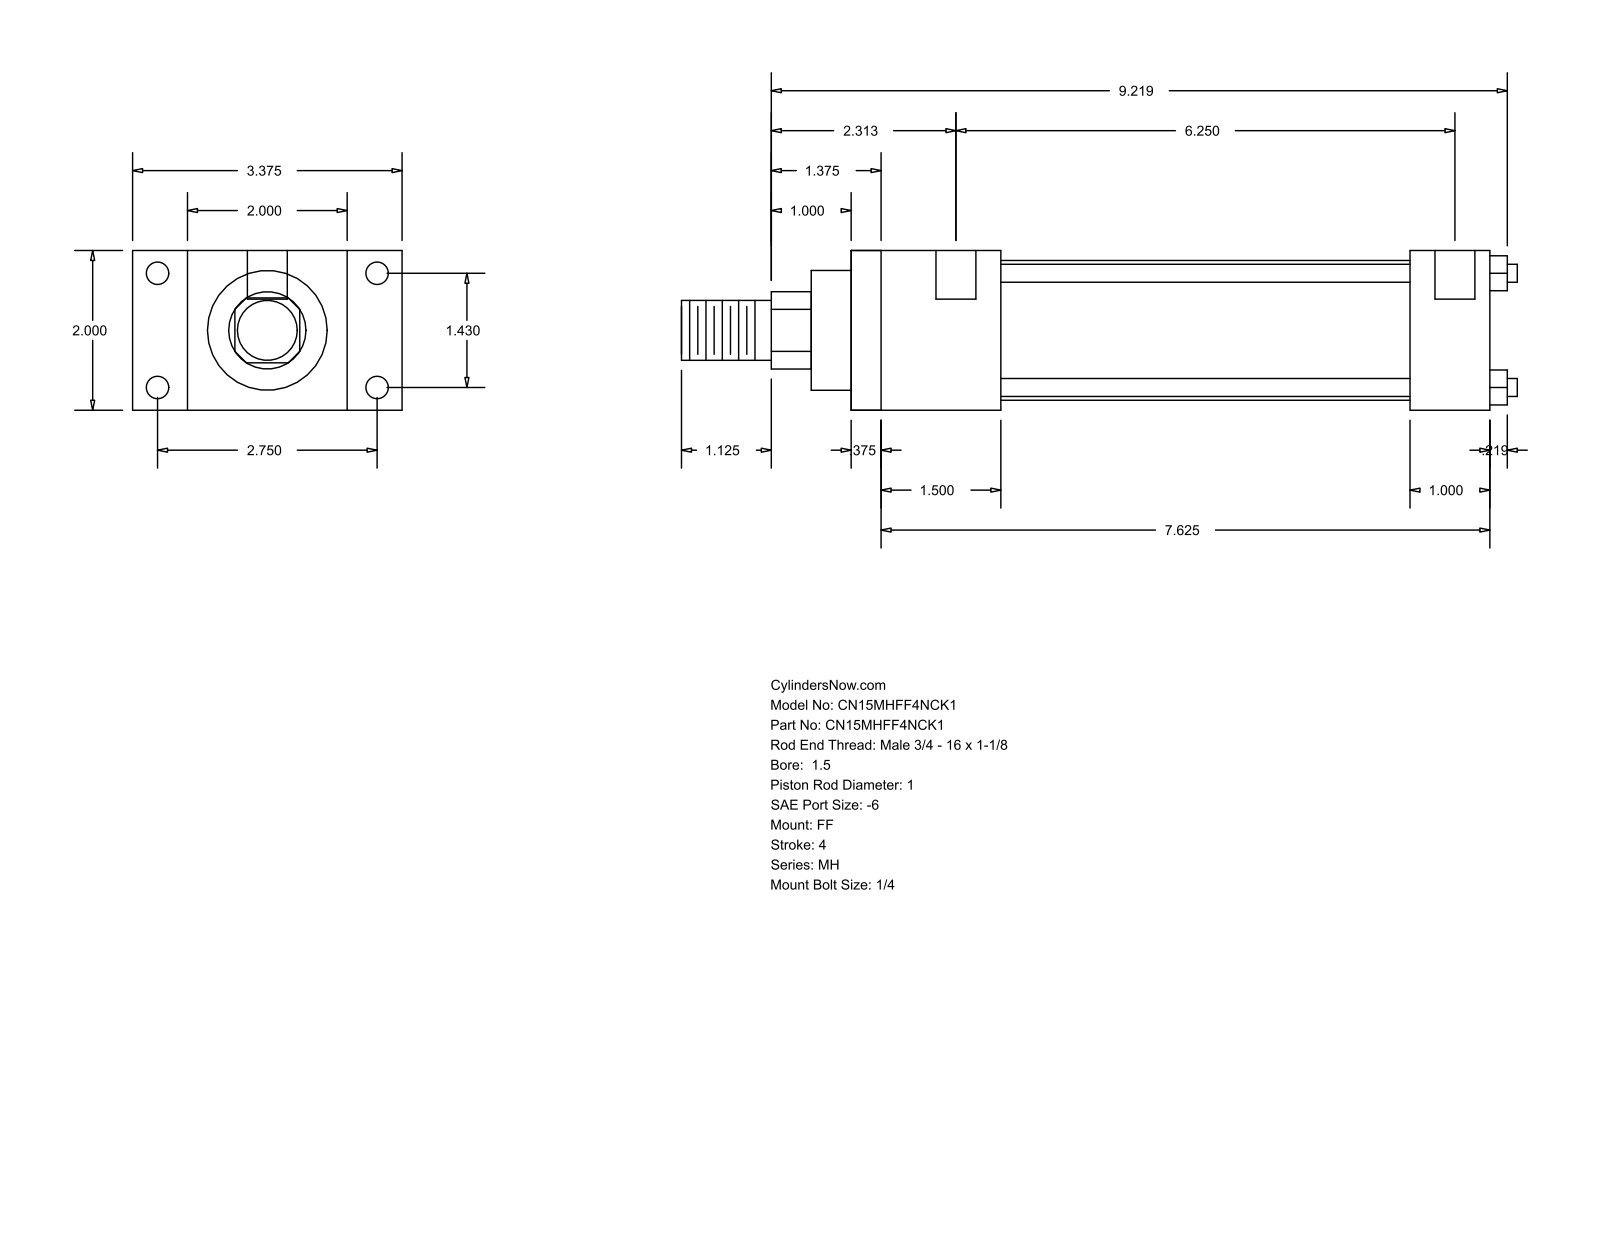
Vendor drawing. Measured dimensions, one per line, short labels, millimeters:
name: MH_FF__0150_1
written by: GSSL Pune (CONFIG_CONTROL_DESIGN)
unit: mm
bodies: 0 solids, 92 faces (64 planar, 28 cylindrical, 0 other)
size: 265.91 × 85.72 × 50.8
holes: 4× ⌀5.56, 4× ⌀7.14, 2× ⌀12.7
bosses: 4× ⌀5.71, 1× ⌀44.45, 1× ⌀38.1, 1× ⌀25.4, 1× ⌀19.05
rounds: 1× R12.29
face distances: 50.8, 203.2, 9.52, 193.68, 25.4, 17.46, 68.26, 47.63, 38.11, 155.57
hole spacings: 36.32, 69.84, 78.72, 161.93, 3.18, 158.75
